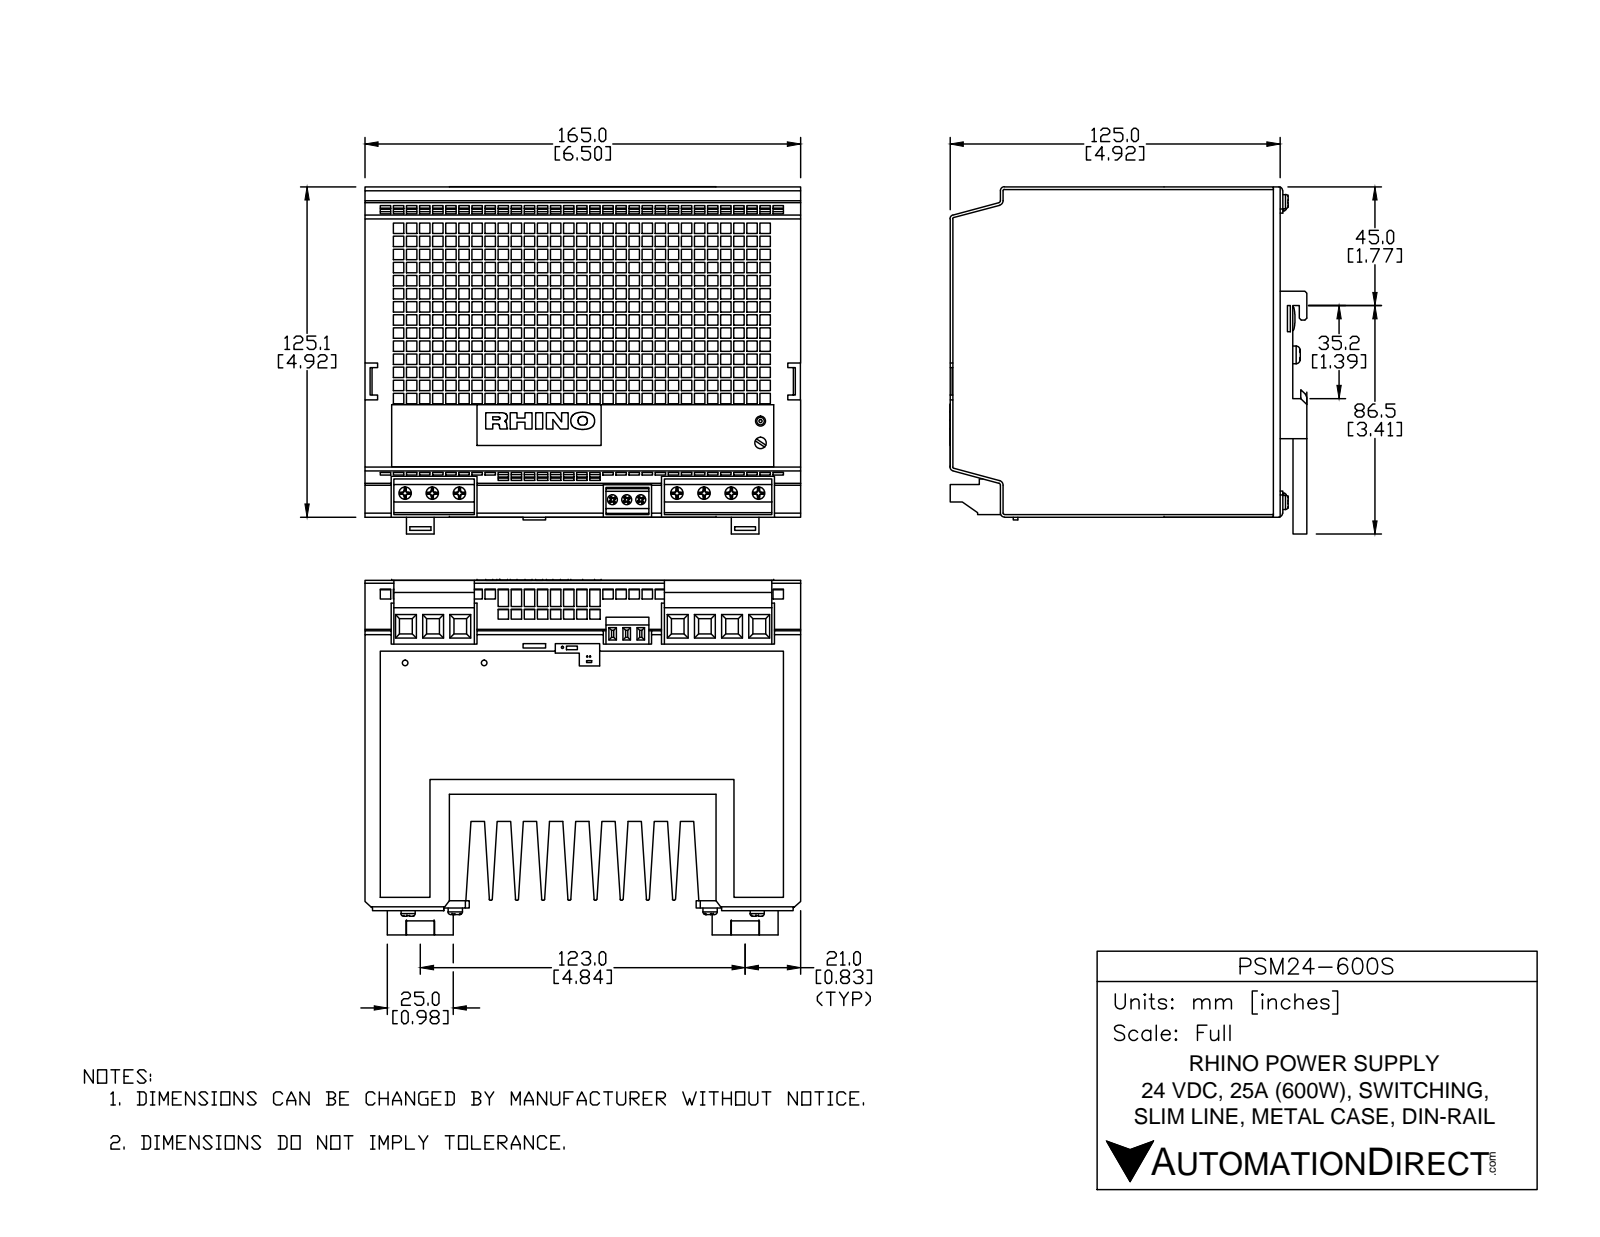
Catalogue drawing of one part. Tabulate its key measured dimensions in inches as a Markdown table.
| quantity | value |
| --- | --- |
| part name | PSM24-600S |
| STEP written by | SolidWorks 2011 (CONFIG_CONTROL_DESIGN) |
| units | inches |
| bodies | 1 solid, 5451 faces (5237 planar, 125 cylindrical, 89 other) |
| overall size | 6.49 × 5.281 × 5.181 |
| volume | 136.1 in³ |
| surface area | 310.1 in² |
| round holes (diameter × count) | 0.185 × 7, 0.15 × 3, 0.08 × 2, 0.15 × 1, 0.172 × 1 |
| round bosses / shafts (diameter × count) | 0.212 × 4, 0.21 × 4, 0.265 × 2, 0.109 × 1, 0.033 × 1, 0.021 × 1, 0.02 × 1 |
| partial cylindrical surfaces (radius × count) | 0.06 × 26, 0.015 × 16, 0.02 × 4, 0.03 × 4, 0.07 × 2 |
| main face-to-face distances | 0.778, 1.168, 0.389, 0.389, 1.946, 1.557, 1.557, 2.335, 6.488, 2.724 |
| hole center spacings | 0.405, 4.05, 0.405, 0.81, 4.455, 0.21, 0.21, 0.324 |
